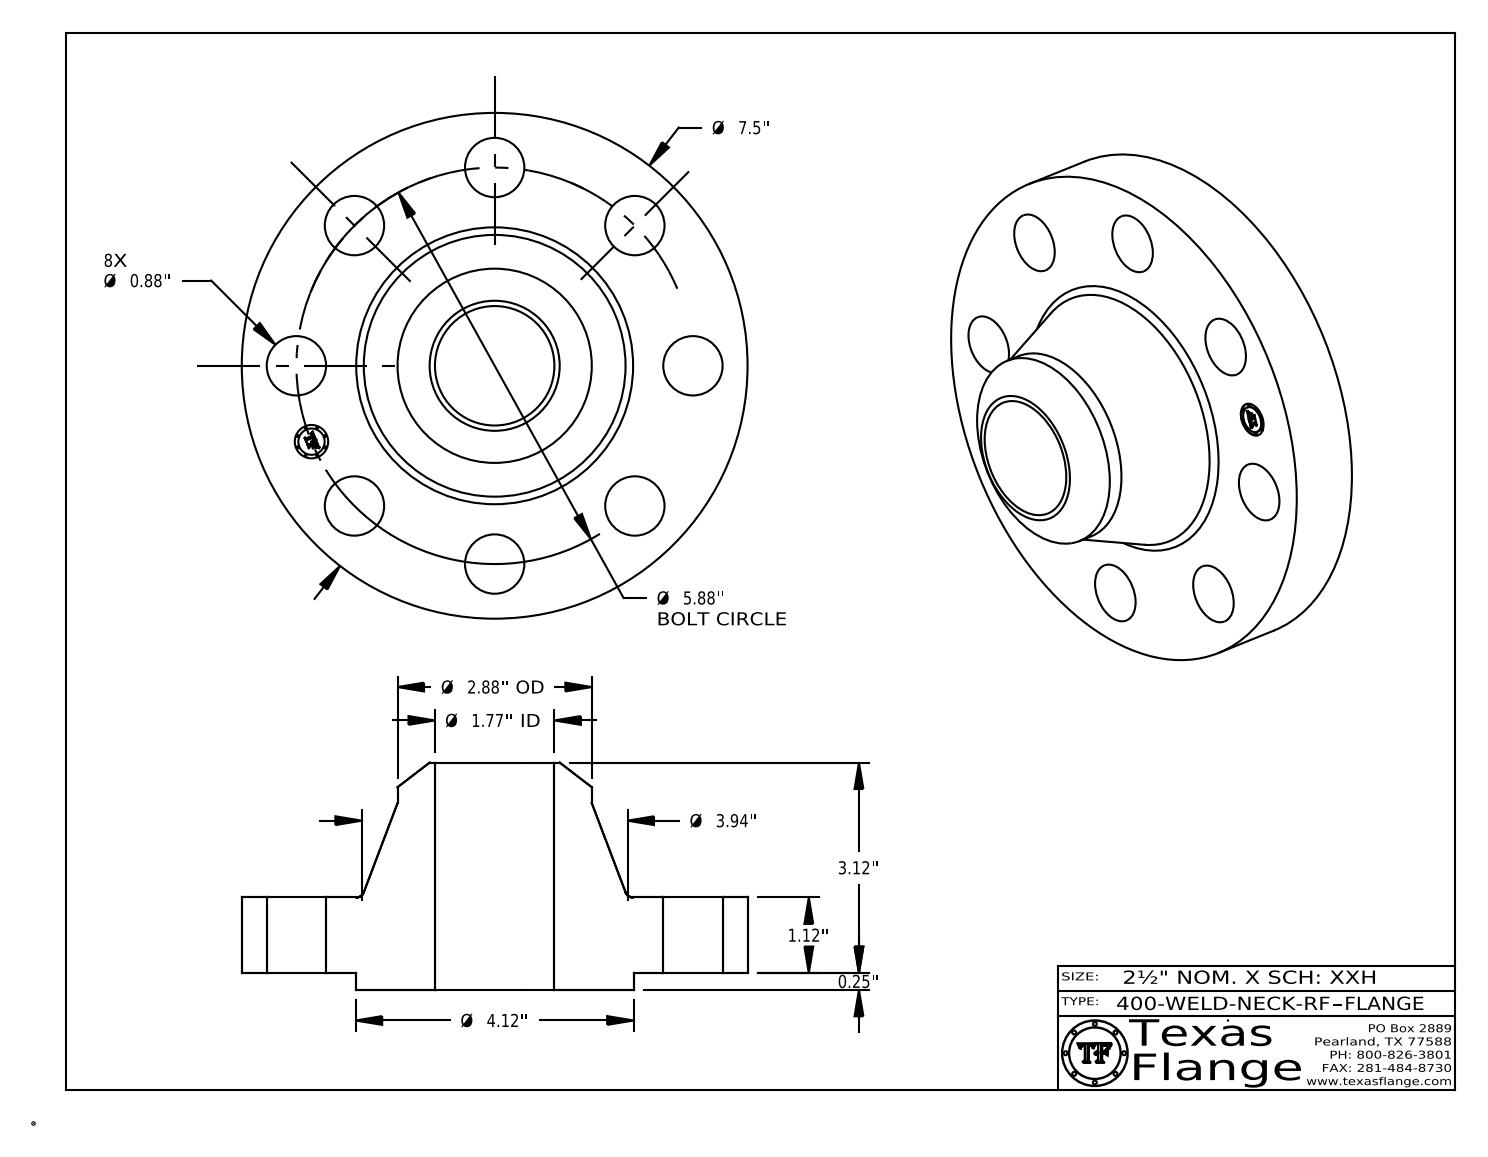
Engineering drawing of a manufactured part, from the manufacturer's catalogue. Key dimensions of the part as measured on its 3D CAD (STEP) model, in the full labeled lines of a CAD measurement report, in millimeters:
Part name (STEP PRODUCT): 400-WELD-NECK-RF
STEP written by: CATIA V5 STEP AP214 (AUTOMOTIVE_DESIGN)
Units: millimetres
Bodies: 1 solid, 419 faces (369 planar, 44 cylindrical, 6 other)
Overall size (bounding box): 190.5 × 190.5 × 85.6
Volume: 904 100 mm³ · Surface area: 103 300 mm²
Round holes (diameter × count): ⌀22.4 ×8, ⌀12.6 ×1, ⌀45 ×1
Round bosses / shafts (diameter × count): ⌀0.8 ×8, ⌀190.5 ×1, ⌀104.6 ×1, ⌀73.2 ×1, ⌀9.9 ×1
Main face-to-face distances: 28.4, 6.4, 34.8, 85.6, 79.2, 50.8, 0.4, 34.4, 28.1, 51.2
Hole centre spacings: 57.2, 138, 74.7, 74.7, 105.6, 105.6, 83, 149.4
